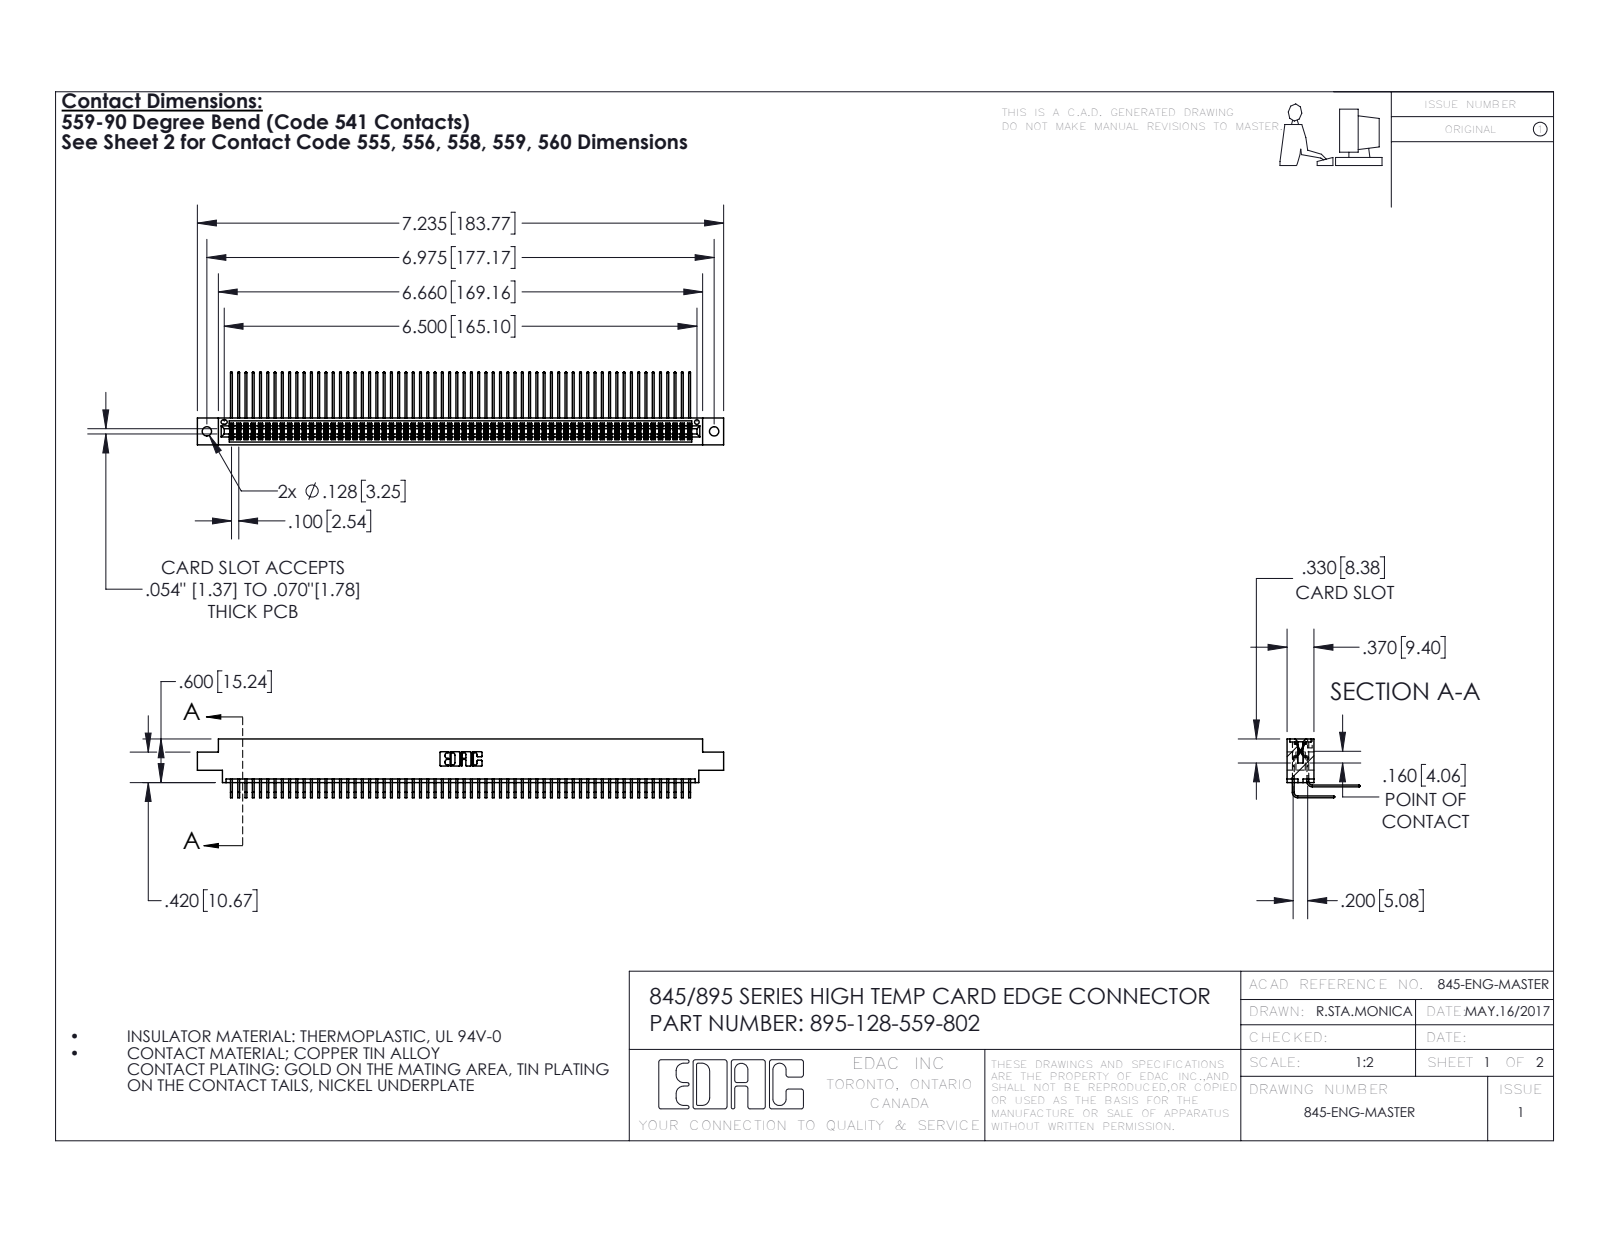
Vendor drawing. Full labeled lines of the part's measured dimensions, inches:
Part name (STEP PRODUCT): 395-128-559-802; 345 Part_0.170 Offset - 0.128 Dia; 345-292-001_558 559 Tail - 1; 345-292-001_559 Tail - 2
STEP written by: SolidWorks 2016 (CONFIG_CONTROL_DESIGN)
Units: inches
Bodies: 129 solids, 6786 faces (4564 planar, 2222 cylindrical, 0 other)
Overall size (bounding box): 7.235 × 1.005 × 0.809
Volume: 1.138 in³ · Surface area: 48.56 in²
Round holes (diameter × count): ⌀0.128 ×2, ⌀0.064 ×1
Partial cylindrical surfaces — rounded edges, fillets, slot ends (radius × count): R0.006 ×192, R0.01 ×22, R0.007 ×6, R0.031 ×6, R0.026 ×3, R0.014 ×2, R0.019 ×2, R0.022 ×2
Main face-to-face distances: 0.072, 0.298, 0.37, 0.2, 0.098, 0.272, 0.025, 0.225, 0.175, 0.15
Hole centre spacings: 0.27, 6.739, 6.975
